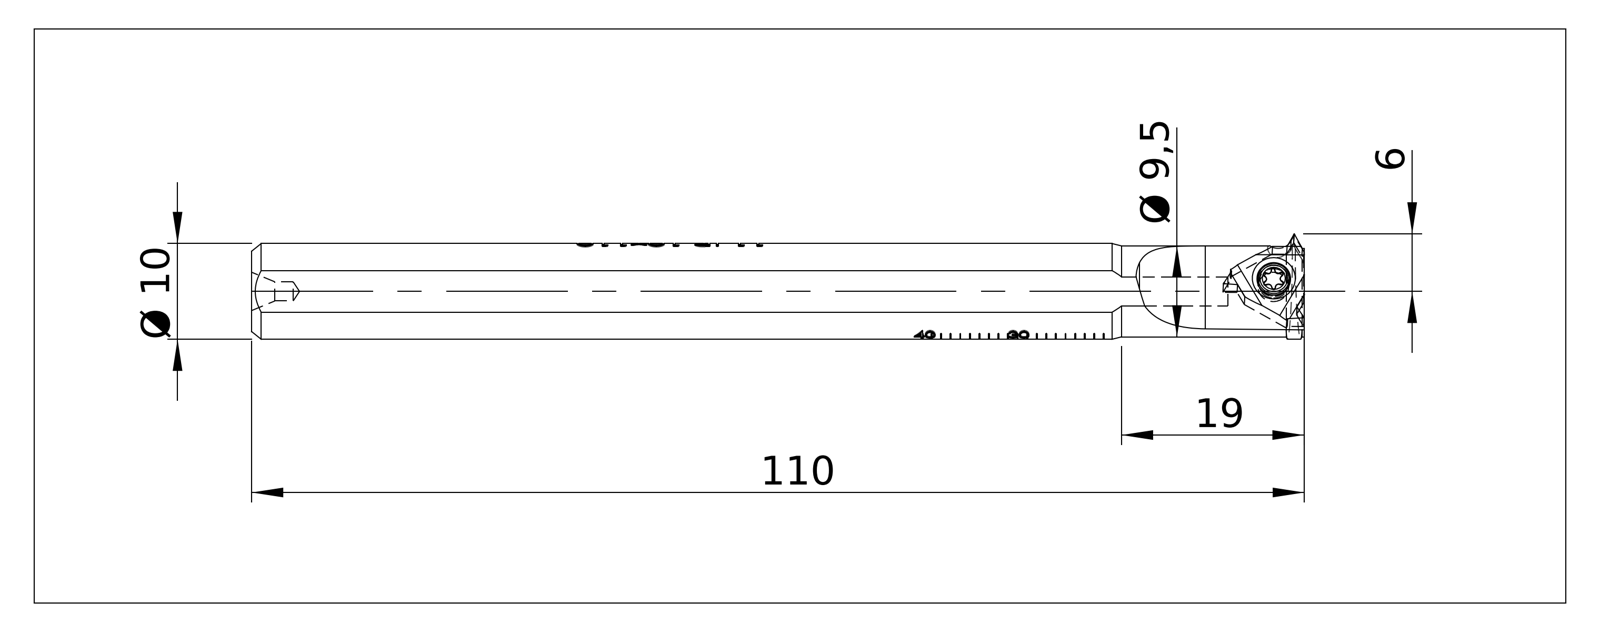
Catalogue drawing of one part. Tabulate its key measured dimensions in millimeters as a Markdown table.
| quantity | value |
| --- | --- |
| part name | NOCUT; CL-11IR 10x110; CUT |
| STEP written by | SolidWorks 2020 (AUTOMOTIVE_DESIGN) |
| units | millimeters |
| bodies | 2 solids, 332 faces (200 planar, 64 cylindrical, 68 other) |
| overall size | 110 × 11.01 × 10.34 |
| volume | 7 975 mm³ |
| surface area | 3 735 mm² |
| round holes (diameter × count) | 2 × 1, 3.2 × 1 |
| round bosses / shafts (diameter × count) | 9.5 × 1 |
| partial cylindrical surfaces (radius × count) | 0.16 × 6, 0.32 × 6, 1 × 3, 1.52 × 1, 4.9 × 1, 5 × 1, 5.33 × 1, 10 × 1 |
| main face-to-face distances | 9, 109.97, 2.8, 0.38, 3.18, 3.67, 7.85, 4.18, 3.64, 7.86 |
